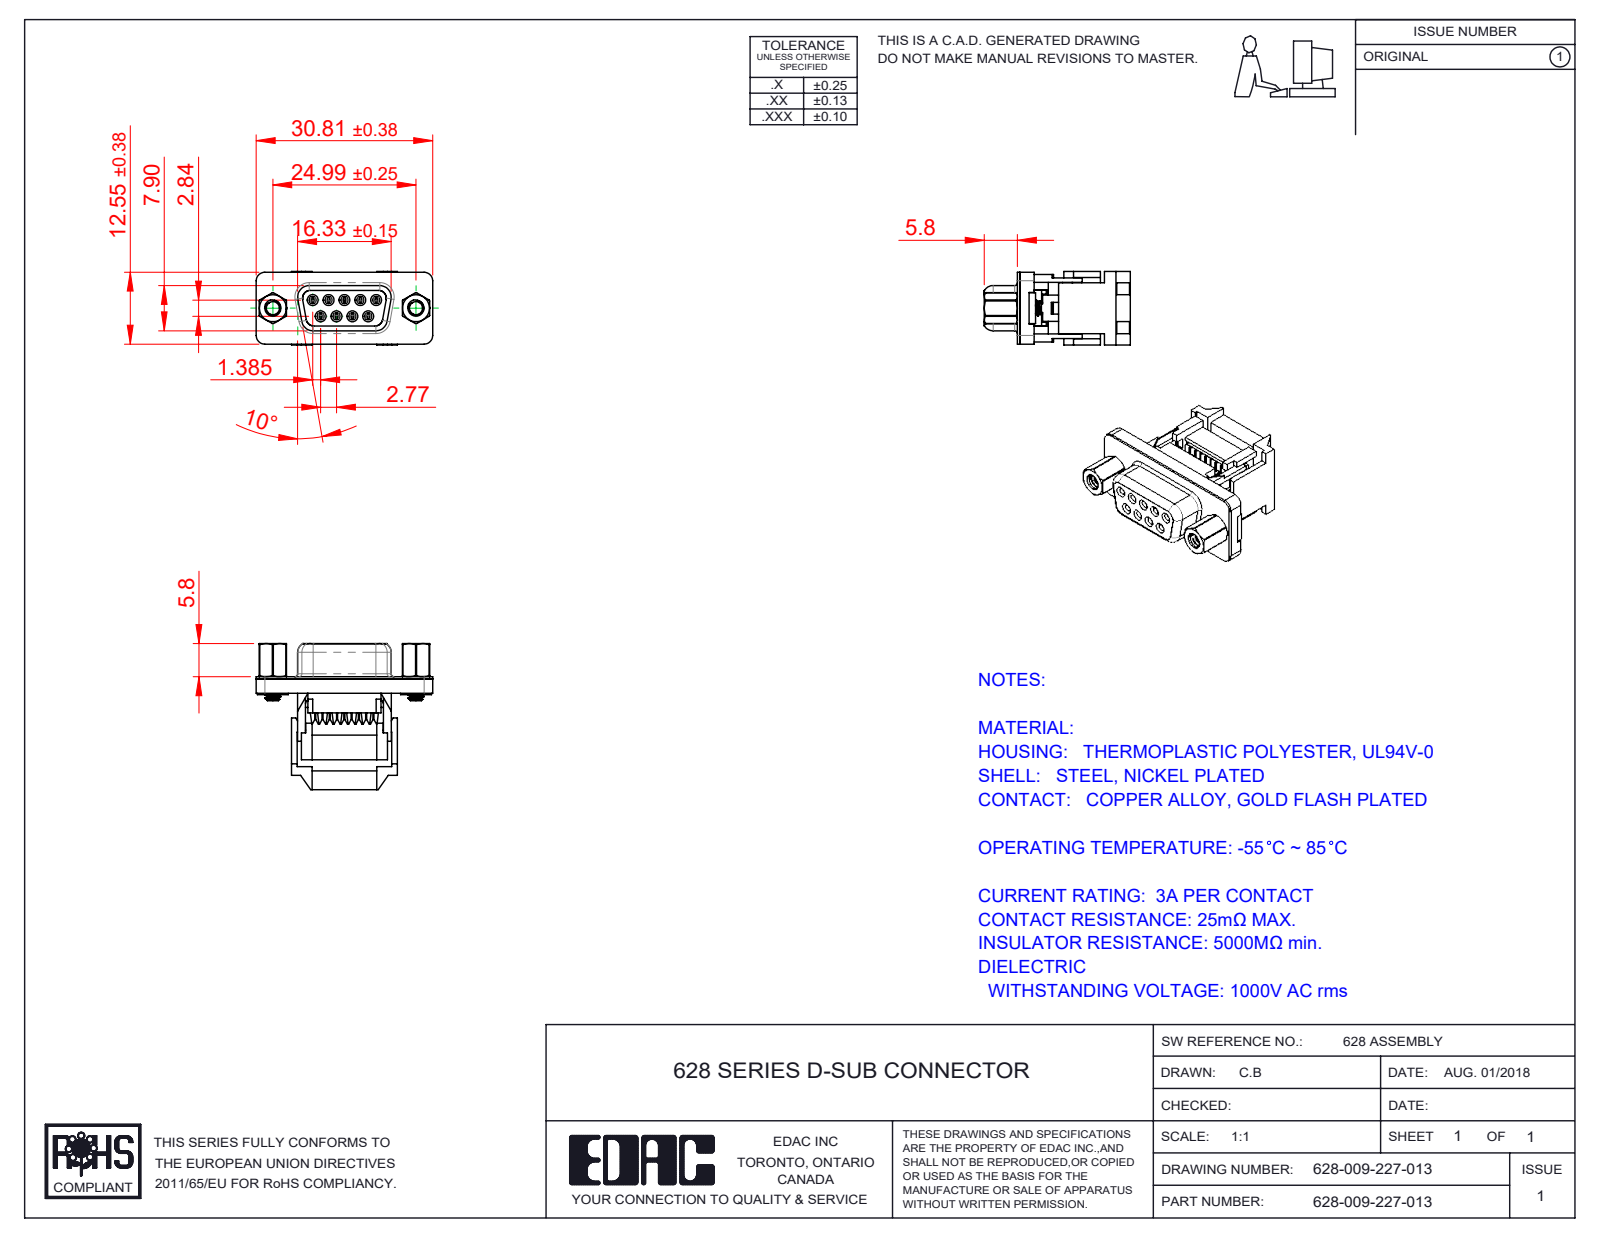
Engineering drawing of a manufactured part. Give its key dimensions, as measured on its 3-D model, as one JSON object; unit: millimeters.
{"part_name": "628 IDC Cable Cover_09 Contacts; 628 4-40 Hex Standoff; 628 IDC 4-40 Threaded Rivet; 628 IDC Housing_09 Contacts (+5 more)", "step_written_by": "SolidWorks 2020 (CONFIG_CONTROL_DESIGN)", "units": "millimeters", "bodies": {"solids": 20, "faces": 1909, "planar": 1134, "cylindrical": 435, "other": 340}, "overall_size": [30.81, 25.5, 12.85], "volume_mm3": 3361, "surface_area_mm2": 7125, "round_holes": [[1.2, 9], [2.26, 2], [2.29, 2], [4, 2], [4.8, 2], [5, 2]], "round_bosses_or_shafts": [[4.9, 2], [2.79, 2]], "partial_cylinders_radius": [[0.9, 40], [1.2, 36], [0.5, 22], [0.15, 18], [0.64, 9], [0.65, 9], [0.89, 9], [0.94, 9]], "face_to_face_distances": [1.9, 0.4, 1, 2.9, 2.5, 7.05, 1.06, 5.2, 1.03, 7.07], "hole_center_spacings": [3.16, 2.77, 5.54, 5.03, 5.04, 8.31, 7.48, 7.49]}
